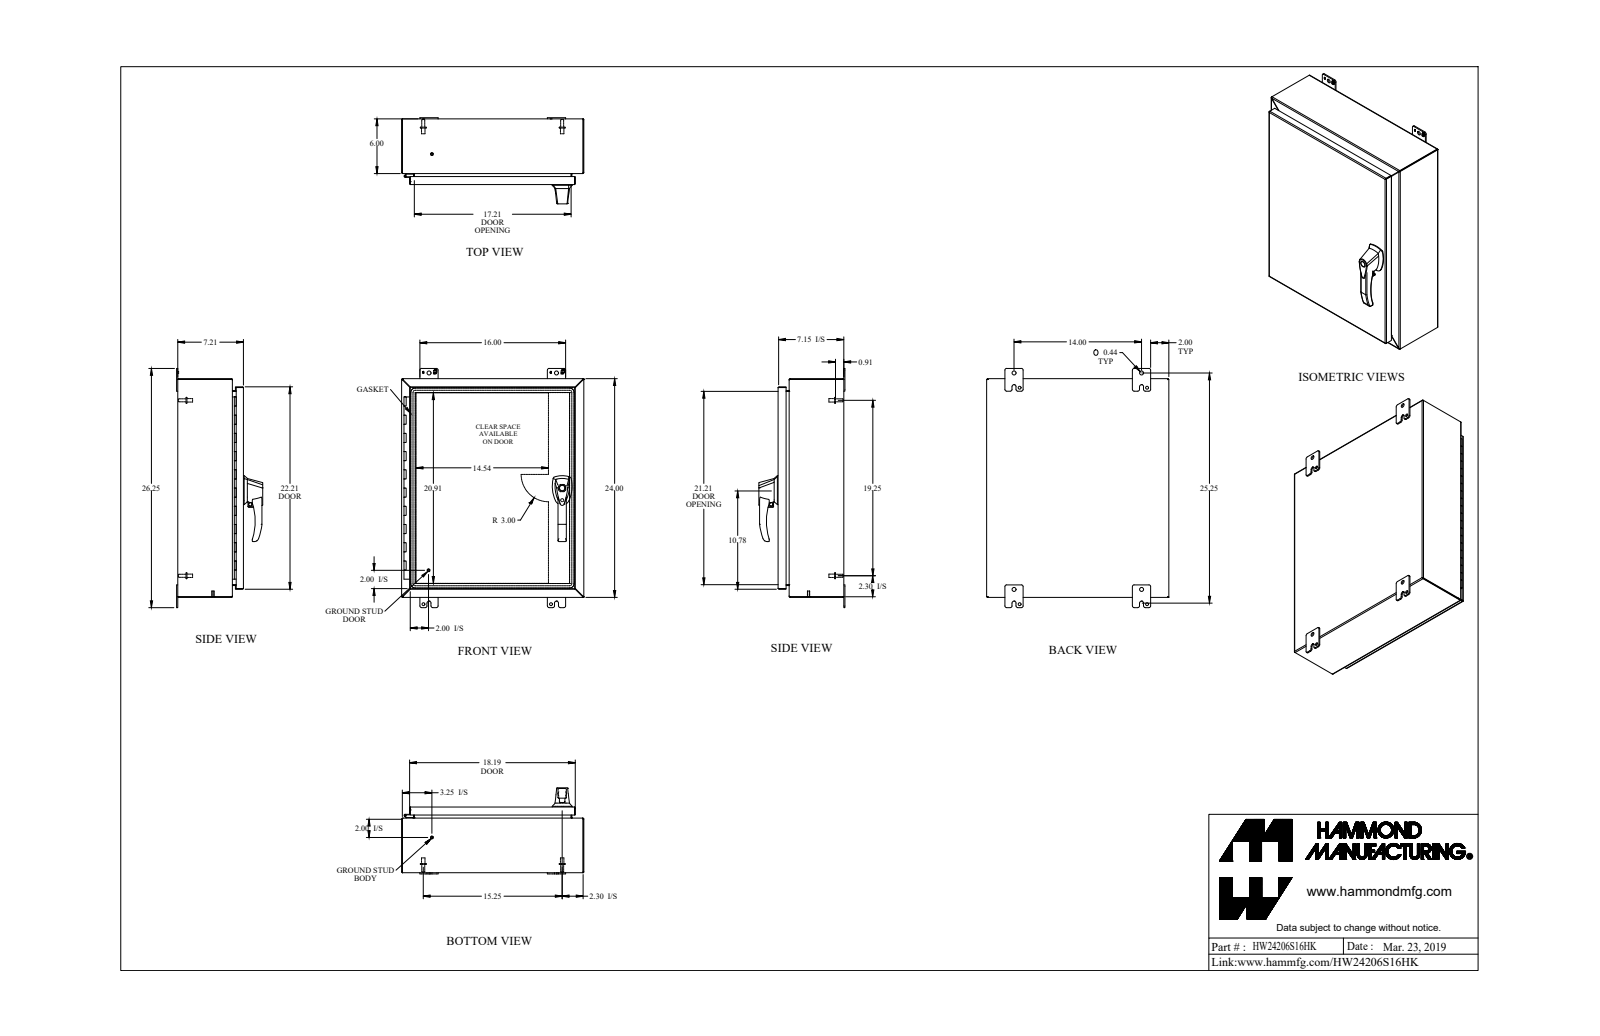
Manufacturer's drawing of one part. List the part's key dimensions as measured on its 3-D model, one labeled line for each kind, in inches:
Part name (STEP PRODUCT): HW24206S16HK
STEP written by: SolidWorks 2018 (AUTOMOTIVE_DESIGN)
Units: inches
Bodies: 46 solids, 1420 faces (688 planar, 580 cylindrical, 152 other)
Overall size (bounding box): 26.25 × 20 × 9.45
Volume: 153 in³ · Surface area: 3 872 in²
Round holes (diameter × count): ⌀0.176 ×6, ⌀0.313 ×5, ⌀0.25 ×3, ⌀0.265 ×3, ⌀0.413 ×3, ⌀0.196 ×2, ⌀0.256 ×2, ⌀0.394 ×2, ⌀0.437 ×2, ⌀0.11 ×1, ⌀0.233 ×1, ⌀0.33 ×1
Round bosses / shafts (diameter × count): ⌀0.375 ×9, ⌀0.25 ×7, ⌀0.156 ×6, ⌀0.65 ×4, ⌀0.332 ×4, ⌀0.313 ×4, ⌀1 ×3, ⌀0.51 ×3
Partial cylindrical surfaces — rounded edges, fillets, slot ends (radius × count): R0.25 ×27, R0.188 ×24, R0.036 ×20, R0.108 ×20, R0.06 ×12, R0.125 ×9, R0.045 ×8, R0.218 ×8
Main face-to-face distances: 0.072, 7.138, 7.066, 0.072, 7.138, 7.21, 19.928, 23.928, 5.928, 19.856
Hole centre spacings: 1.111, 8.118, 8.119, 16.237, 1.338, 6.78, 7.576, 7.577
